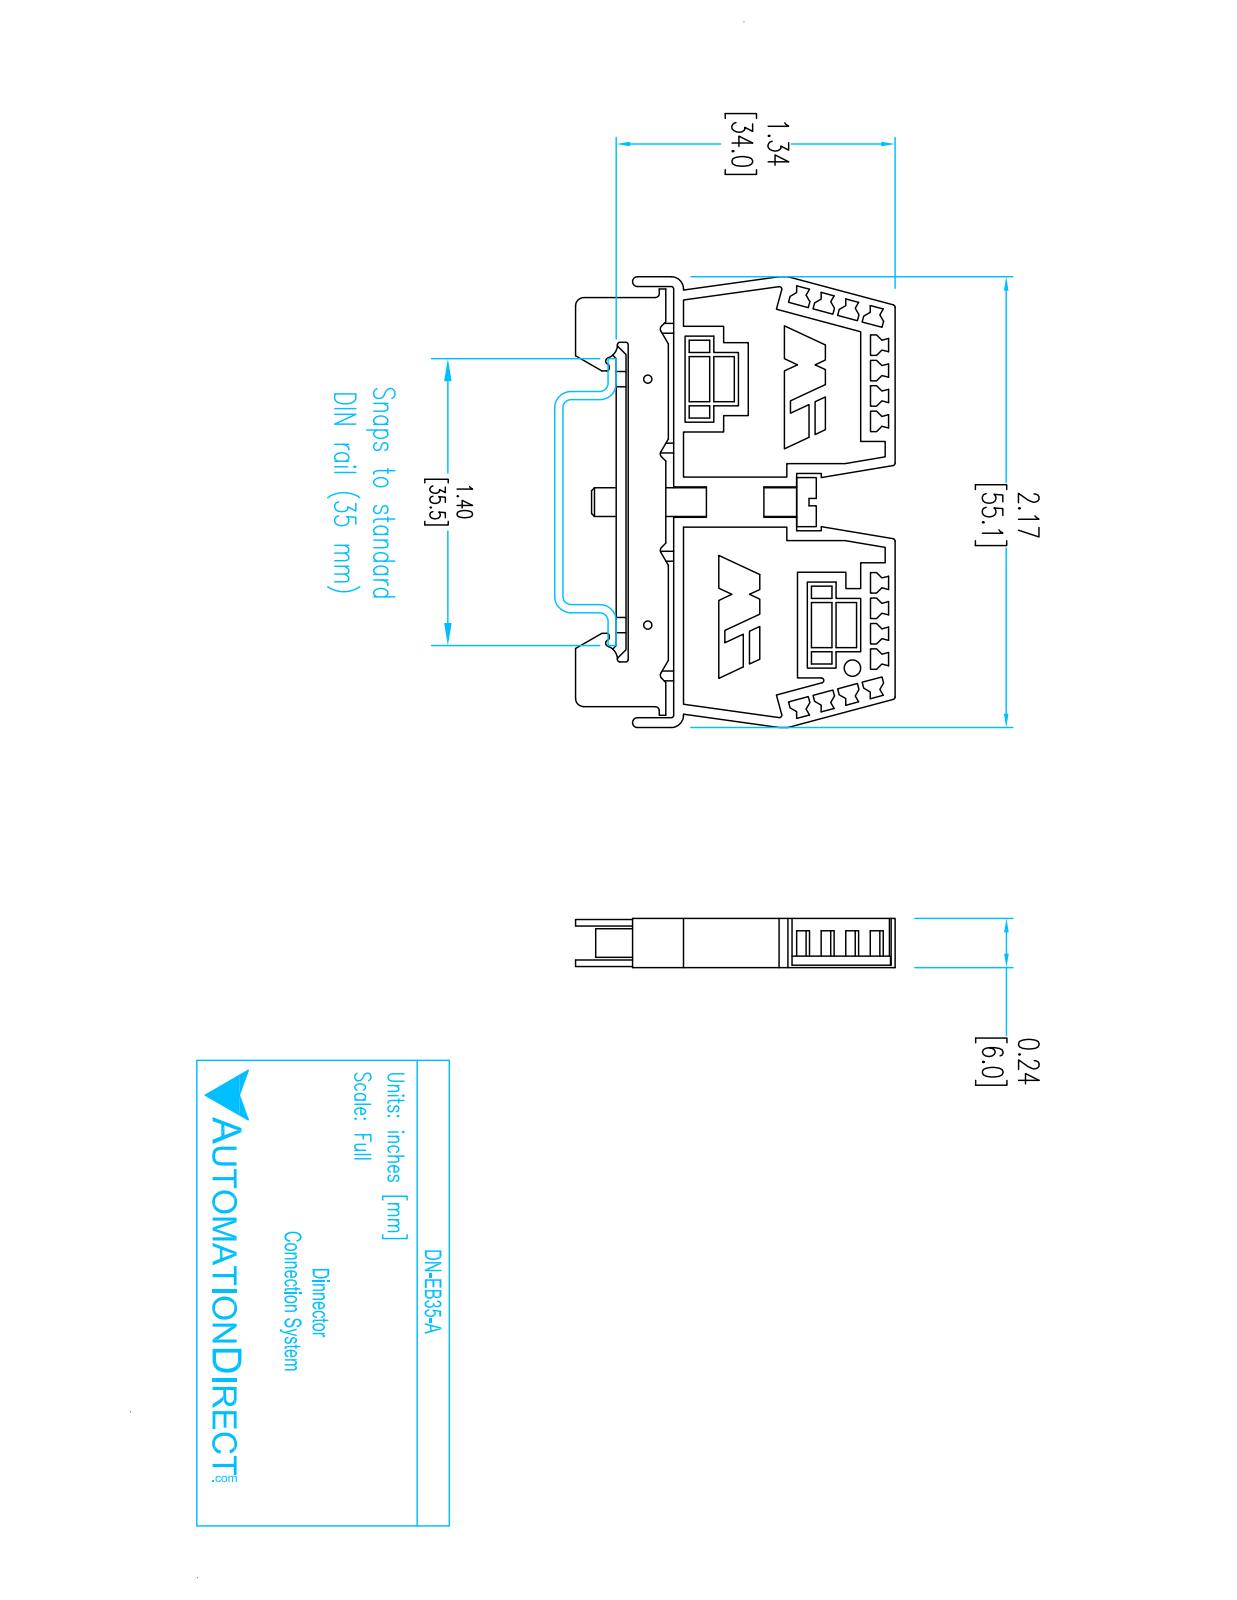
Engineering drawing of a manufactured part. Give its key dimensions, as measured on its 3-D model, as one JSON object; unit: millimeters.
{"part_name": "43444_DN-EB35-A", "step_written_by": "SolidWorks 2013 (AUTOMOTIVE_DESIGN)", "units": "millimeters", "bodies": {"solids": 1, "faces": 406, "planar": 357, "cylindrical": 49, "other": 0}, "overall_size": [55, 38.95, 6], "volume_mm3": 6367, "surface_area_mm2": 7092, "partial_cylinders_radius": [[0.3, 17], [0.5, 6], [0.4, 2], [0.6, 2], [1, 2], [1.5, 2], [1.7, 2], [5, 2]], "face_to_face_distances": [2.25, 3.75, 6, 1.5, 1.2, 0.5, 3, 22.8, 2.5, 2]}
